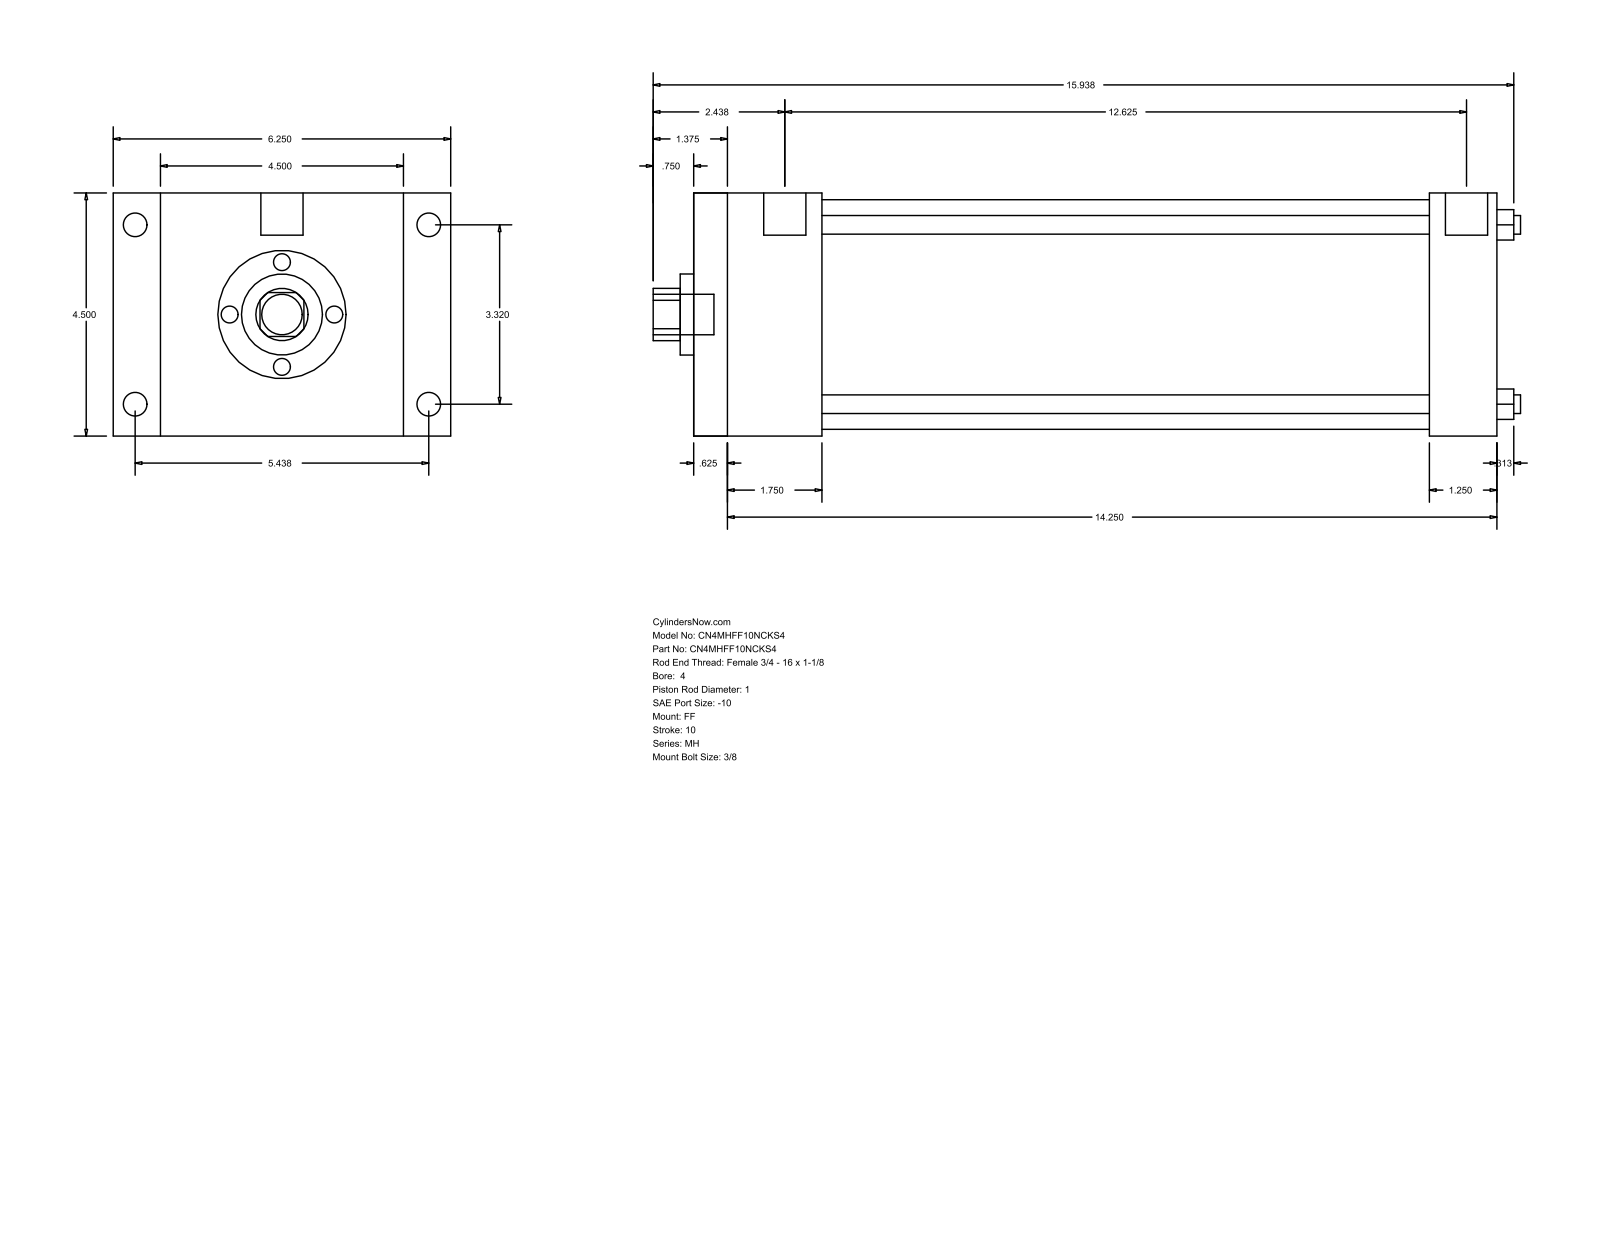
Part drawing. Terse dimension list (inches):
name: MH_FF__0400_1
written by: GSSL Pune (CONFIG_CONTROL_DESIGN)
unit: in
bodies: 0 solids, 92 faces (64 planar, 28 cylindrical, 0 other)
size: 16.063 × 6.25 × 4.5
holes: 4× ⌀0.345, 1× ⌀1, 1× ⌀1.5, 1× ⌀4.25
bosses: 4× ⌀0.438, 4× ⌀0.344, 2× ⌀0.781, 1× ⌀0.75
rounds: 1× R0.484
face distances: 4.5, 14.875, 0.625, 14.25, 2.375, 1.75, 12.5, 13.625, 13, 11.25
hole spacings: 2.347, 3.32, 4.695
